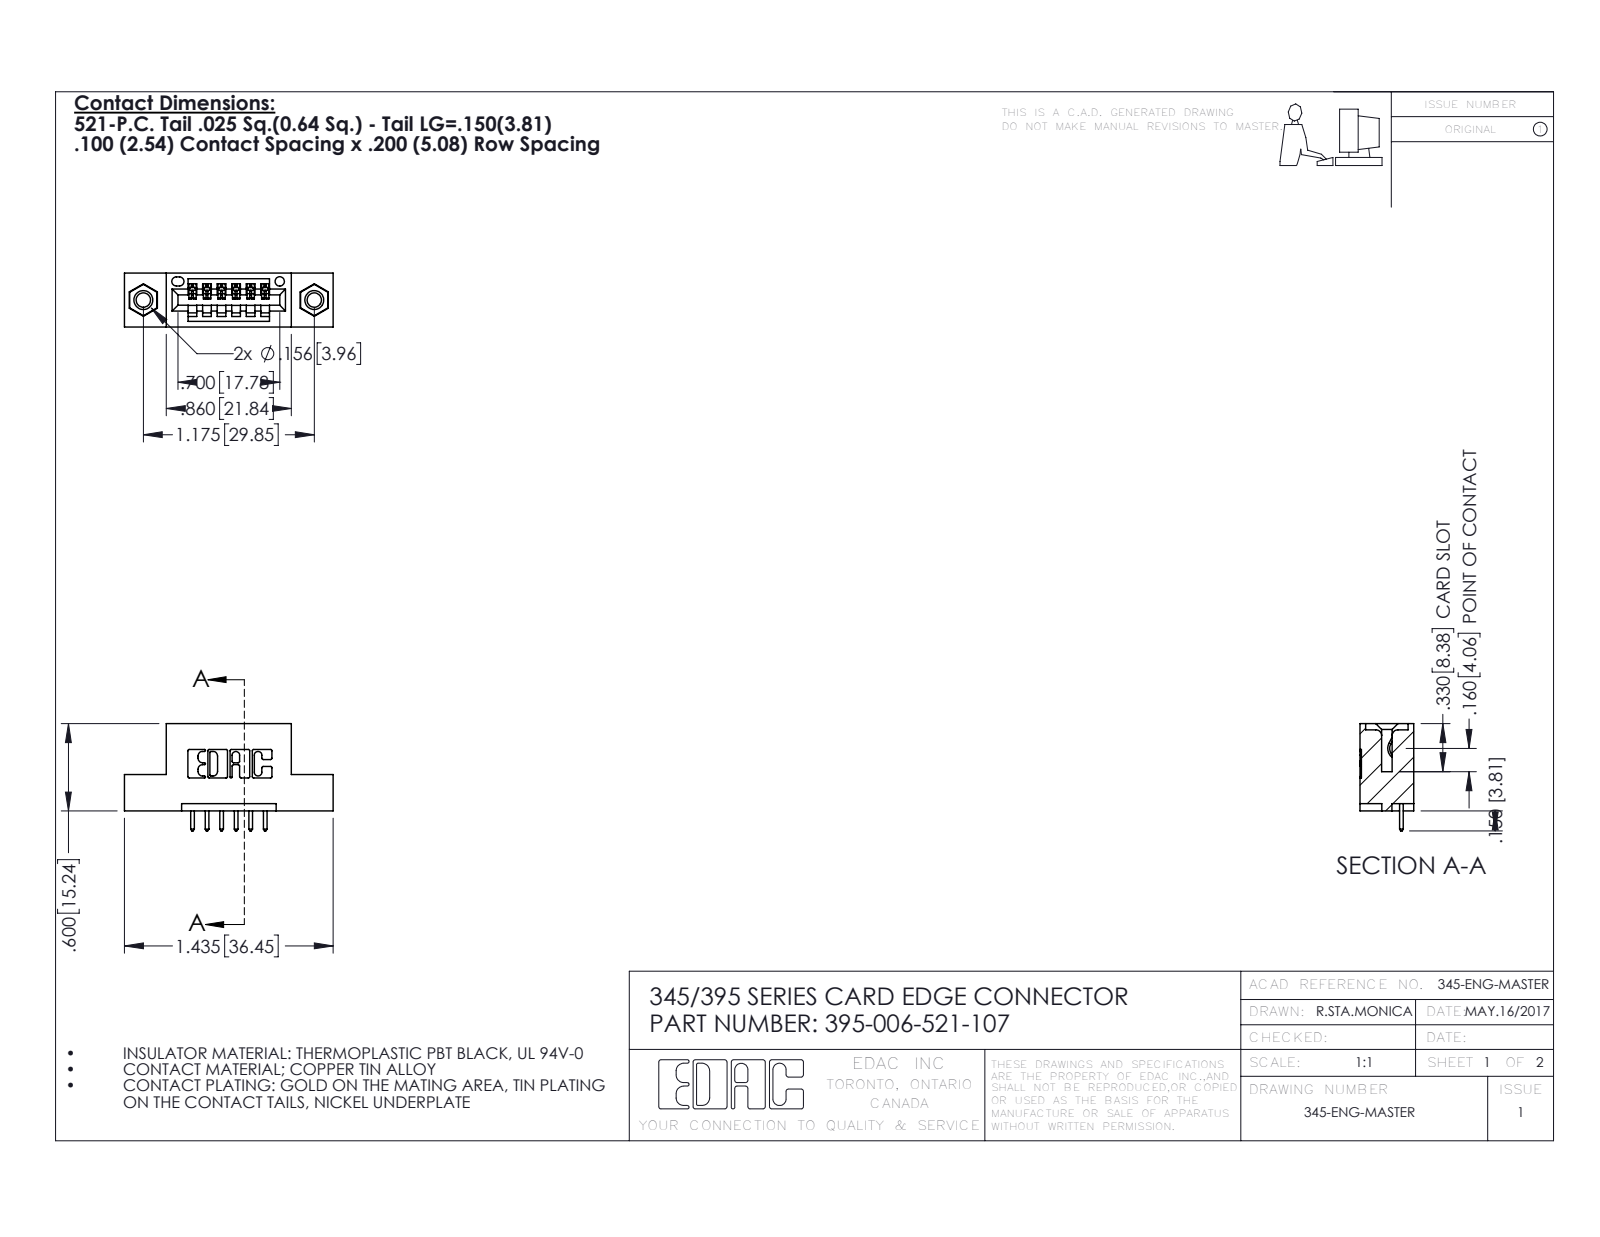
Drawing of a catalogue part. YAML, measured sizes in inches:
part_name: "345-292-001_345-293-121; 395-006-521-107; 345 Part_Flush Mounting Lugs - 0.156 Dia-TI; 345-250-001_345-250-005-103"
step_written_by: "SolidWorks 2016 (CONFIG_CONTROL_DESIGN)"
units: inches
bodies: {solids: 9, faces: 534, planar: 352, cylindrical: 166, other: 16}
overall_size: [1.435, 0.737, 0.37]
volume: 0.191
surface_area: 5.649
round_holes:
  - {diameter: 0.098, count: 2}
  - {diameter: 0.125, count: 2}
  - {diameter: 0.156, count: 2}
  - {diameter: 0.064, count: 1}
round_bosses_or_shafts:
  - {diameter: 0.155, count: 2}
partial_cylinders:
  - {radius: 0.01, count: 22}
  - {radius: 0.006, count: 12}
  - {radius: 0.01, count: 12}
  - {radius: 0.007, count: 6}
  - {radius: 0.031, count: 6}
  - {radius: 0.026, count: 3}
  - {radius: 0.031, count: 2}
  - {radius: 0.04, count: 2}
face_to_face_distances: [0.2, 0.37, 0.072, 0.298, 0.1, 0.025, 0.098, 0.272, 0.06, 0.3]
hole_center_spacings: [0.27, 0.946, 1.175]
